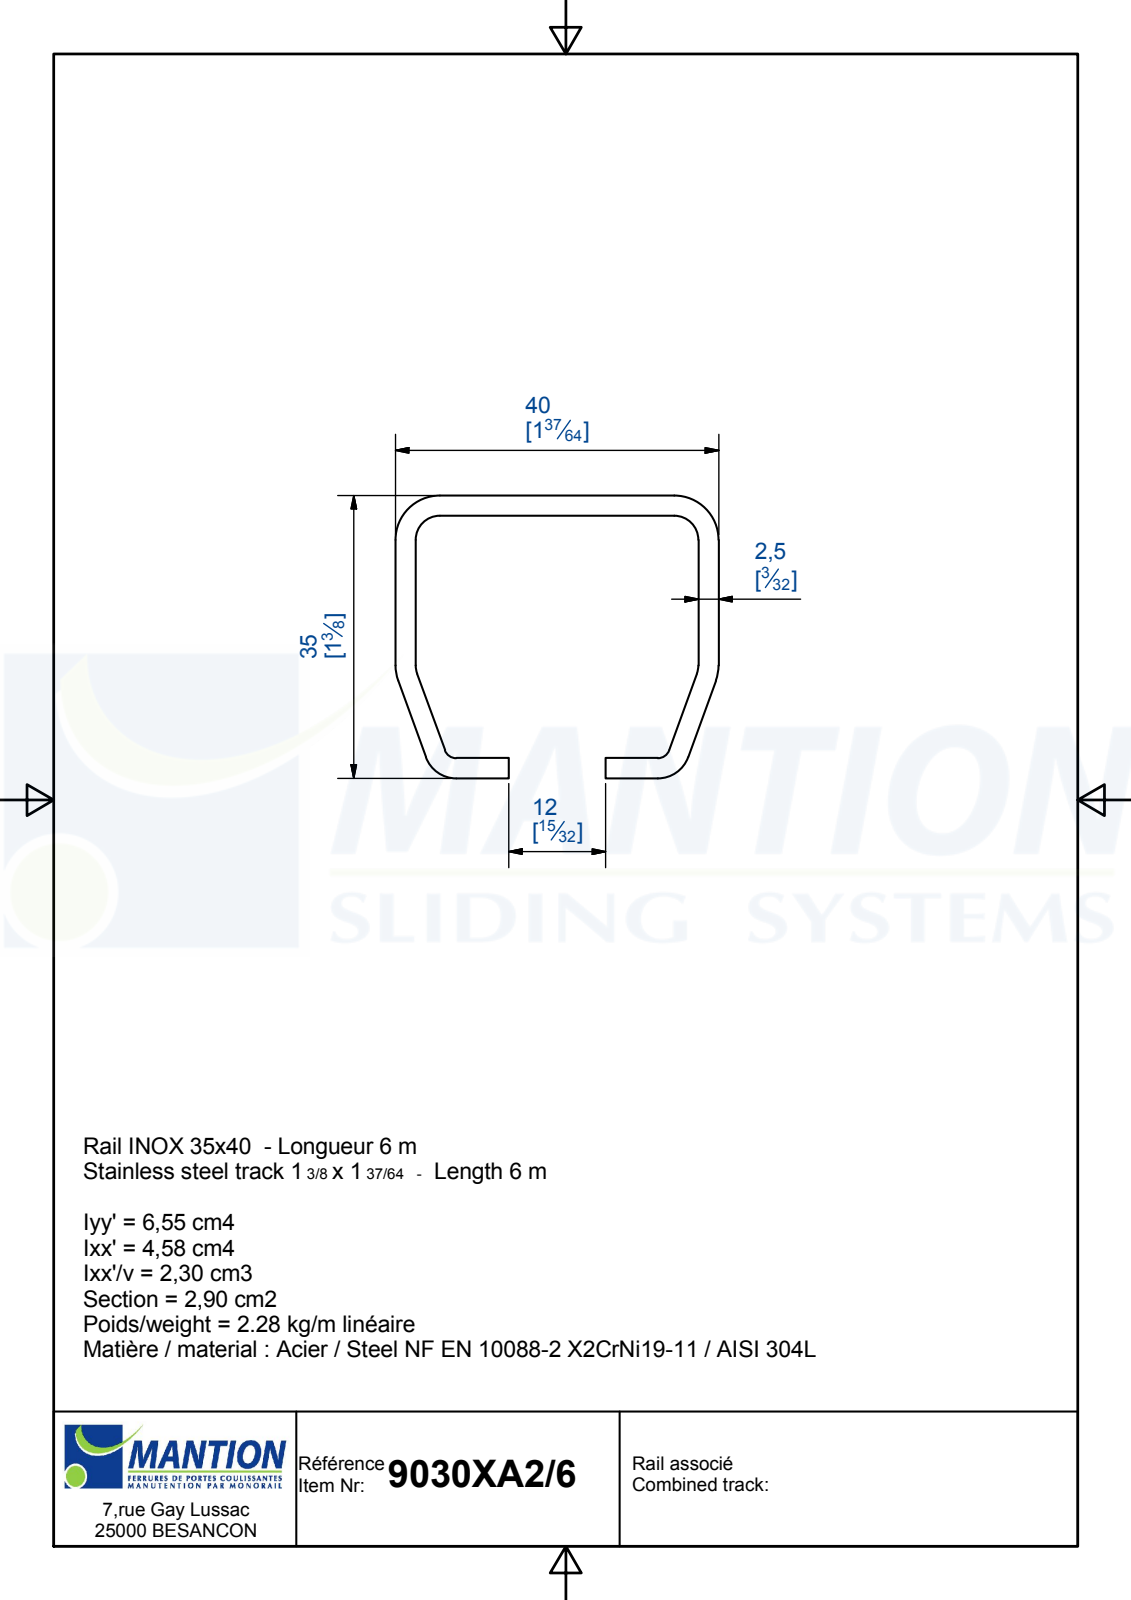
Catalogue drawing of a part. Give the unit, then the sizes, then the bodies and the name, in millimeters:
Units: millimetres
Overall size (bounding box): 6000 × 30 × 28
Partial cylindrical surfaces — rounded edges, fillets, slot ends (radius × count): R1.8 ×4, R3.3 ×4, R2.1 ×2, R3.6 ×2
Main face-to-face distances: 1.5, 28.5, 26.5, 30, 27, 28, 25, 10, 20, 8.5
Volume: 824 383 mm³ · Surface area: 1 117 000 mm²
Bodies: 1 solid, 30 faces (18 planar, 12 cylindrical, 0 other)
Part name (STEP PRODUCT): Rails HERCULE
STEP written by: Autodesk Inventor 2019 (AUTOMOTIVE_DESIGN)
